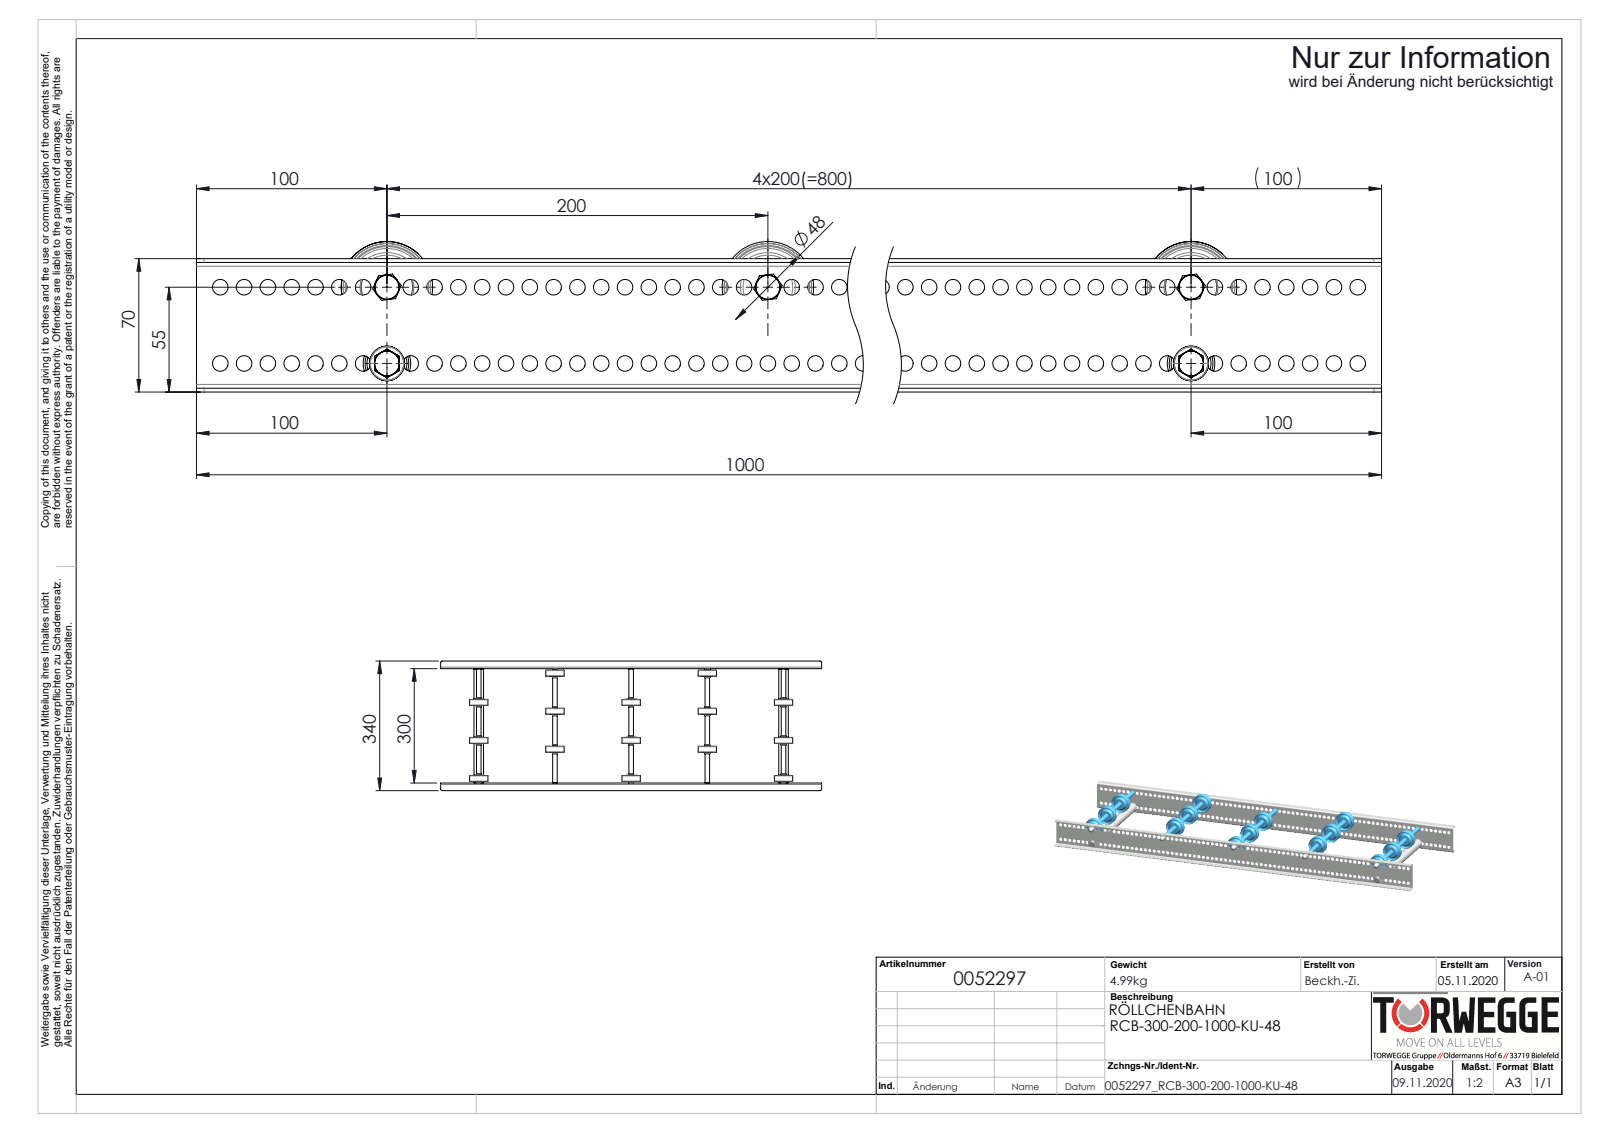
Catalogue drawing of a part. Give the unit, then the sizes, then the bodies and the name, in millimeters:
Units: millimetres
Overall size (bounding box): 1000 × 340 × 79
Round holes (diameter × count): ⌀8.2 ×158, ⌀6.65 ×5, ⌀9.65 ×5, ⌀13.7 ×5, ⌀6.8 ×2, ⌀21 ×2
Round bosses / shafts (diameter × count): ⌀8 ×7, ⌀48 ×5, ⌀27 ×5, ⌀12.7 ×5, ⌀12.5 ×5, ⌀12 ×5, ⌀25 ×2
Partial cylindrical surfaces — rounded edges, fillets, slot ends (radius × count): R4 ×8, R2 ×4
Main face-to-face distances: 2, 302, 68, 304, 300, 66, 70, 99.8, 18, 20
Hole centre spacings: 12.5, 25, 37.5, 50, 62.5, 75, 87.5, 100
Volume: 915 928 mm³ · Surface area: 775 881 mm²
Bodies: 57 solids, 2357 faces (405 planar, 1068 cylindrical, 884 other)
Part name (STEP PRODUCT): S106837_Gewindestange-M8-KFG_L320; 0046278_KB-ROHR-12X1,75mm_KFG_L76; 0052297; 0011532_2300-48-8 (+5 more)
STEP written by: SolidWorks 2020 (AUTOMOTIVE_DESIGN)
